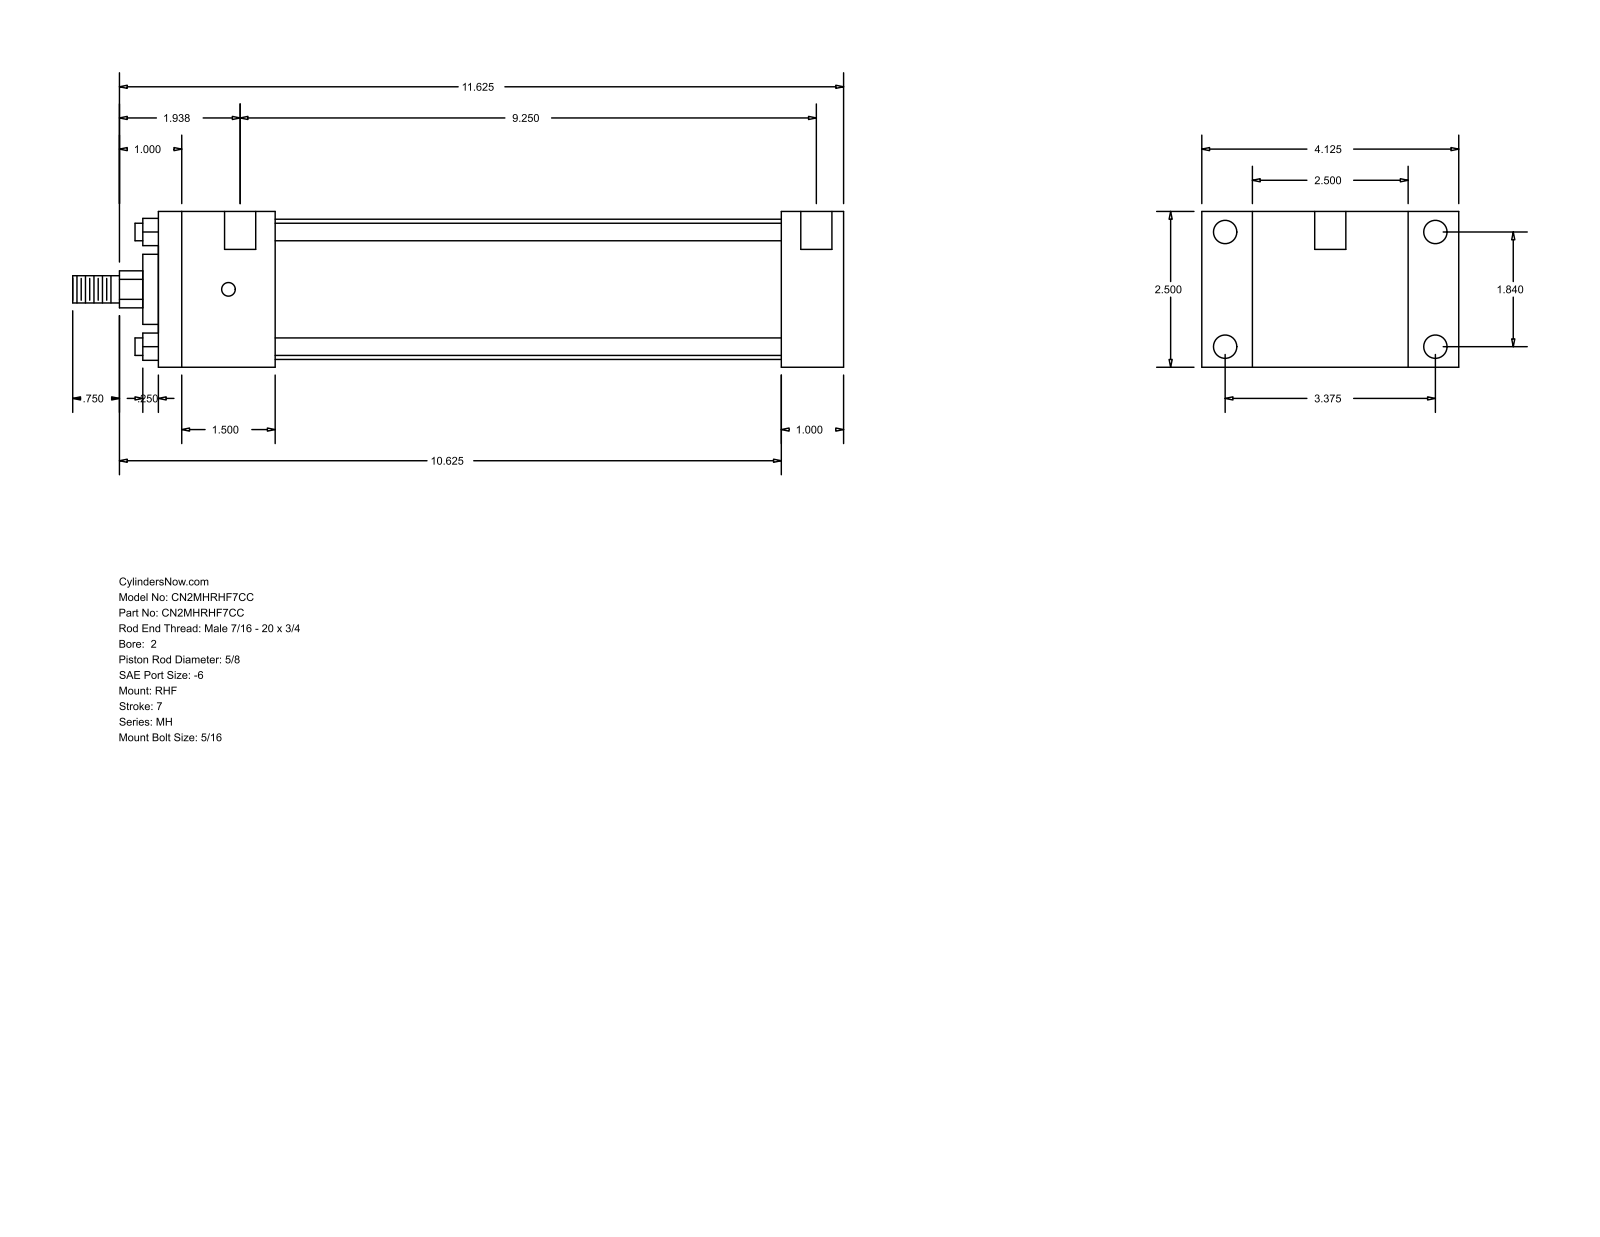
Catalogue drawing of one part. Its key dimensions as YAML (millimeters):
part_name: "MH_RHF__0200_0.625"
step_written_by: "GSSL Pune (CONFIG_CONTROL_DESIGN)"
units: millimeters
bodies: {solids: 0, faces: 88, planar: 60, cylindrical: 28, other: 0}
overall_size: [314.32, 104.78, 63.5]
round_holes:
  - {diameter: 5.56, count: 4}
  - {diameter: 9.53, count: 4}
  - {diameter: 12.7, count: 2}
round_bosses_or_shafts:
  - {diameter: 7.14, count: 4}
  - {diameter: 57.15, count: 1}
  - {diameter: 28.57, count: 1}
  - {diameter: 15.88, count: 1}
  - {diameter: 11.11, count: 1}
partial_cylinders:
  - {radius: 7.54, count: 1}
face_to_face_distances: [63.5, 25.39, 20.64, 84.14, 254, 279.39, 104.78, 47.62, 206.38, 231.77]
hole_center_spacings: [46.74, 85.72, 97.63, 242.89, 3.18, 4.76, 234.95, 238.13]
